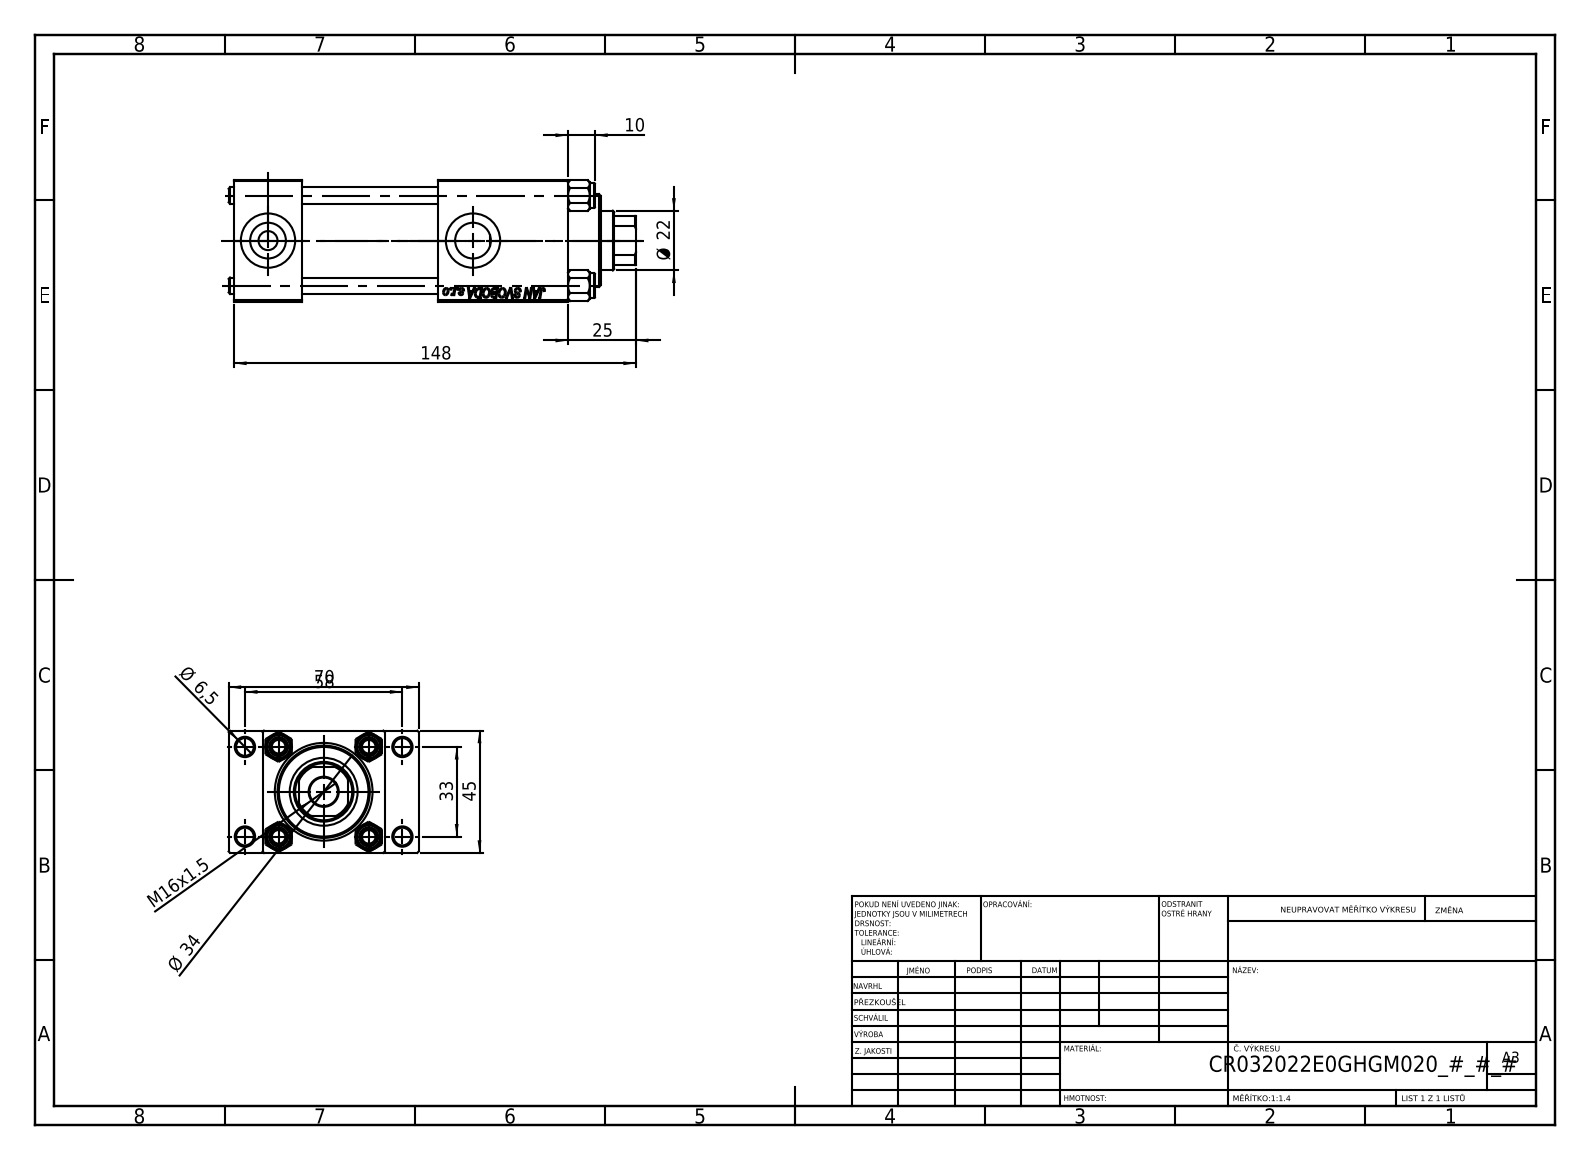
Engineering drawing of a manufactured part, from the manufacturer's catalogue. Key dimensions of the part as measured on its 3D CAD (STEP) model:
Part name (STEP PRODUCT): NUT_M5_E; V215CR_E_Body; V215CR_TYCINKA_E; V215CR_VCP_E (+1 more)
STEP written by: SolidWorks 2019 (CONFIG_CONTROL_DESIGN)
Units: millimetres
Bodies: 11 solids, 1135 faces (497 planar, 86 cylindrical, 552 other)
Overall size (bounding box): 150 × 70 × 45
Volume: 236 088 mm³ · Surface area: 80 866 mm²
Round holes (diameter × count): ⌀6 ×4, ⌀6.5 ×4, ⌀7 ×2, ⌀13.16 ×2, ⌀20 ×2, ⌀10.5 ×1, ⌀22 ×1, ⌀24 ×1, ⌀25 ×1, ⌀32 ×1, ⌀33 ×1
Round bosses / shafts (diameter × count): ⌀9 ×4, ⌀38 ×1, ⌀34 ×1
Partial cylindrical surfaces — rounded edges, fillets, slot ends (radius × count): R10.5 ×1
Main face-to-face distances: 45, 25, 12.5, 57.5, 123, 50, 75, 98, 48, 94.3
Hole centre spacings: 12.4, 23.48, 33.2, 33.37, 35.35, 45.6, 56.35, 33
